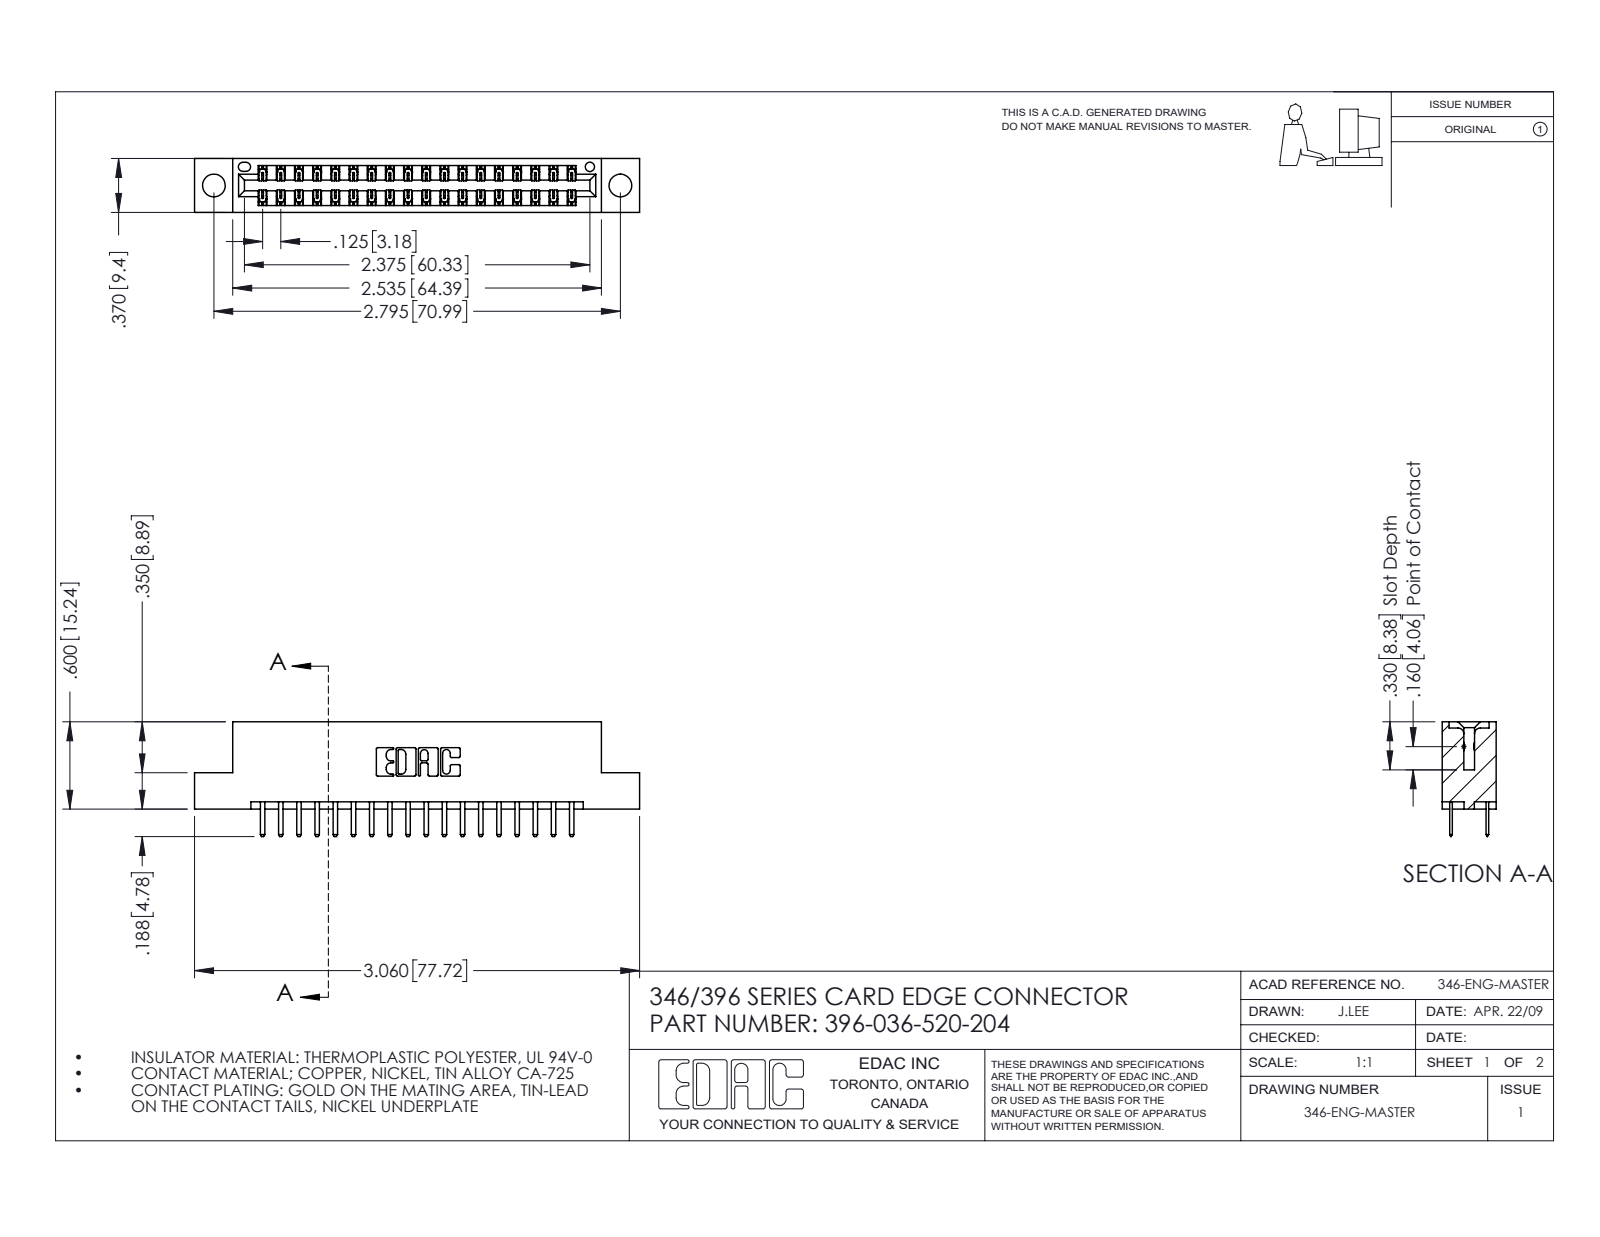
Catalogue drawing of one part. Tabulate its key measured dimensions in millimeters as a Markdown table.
| quantity | value |
| --- | --- |
| part name | 346 Part_Flush Mounting Lugs - 0.156 Dia-TH; 396-036-520-204; 345-292-001_345-293-120 |
| STEP written by | SolidWorks 2016 (CONFIG_CONTROL_DESIGN) |
| units | millimeters |
| bodies | 37 solids, 2138 faces (1408 planar, 730 cylindrical, 0 other) |
| overall size | 77.7 × 20 × 9.4 |
| volume | 7 290 mm³ |
| surface area | 9 419 mm² |
| round holes (diameter × count) | 4 × 2, 1.6 × 1 |
| partial cylindrical surfaces (radius × count) | 0.2 × 54, 0.3 × 40, 0.3 × 22, 0.2 × 6, 0.8 × 6, 0.7 × 3, 0.4 × 2, 0.6 × 2 |
| main face-to-face distances | 6.4, 1.2, 8.2, 9.4, 7, 1.8, 7.6, 0.6, 3.8, 5.6 |
| hole center spacings | 6.2, 65.7, 71 |
